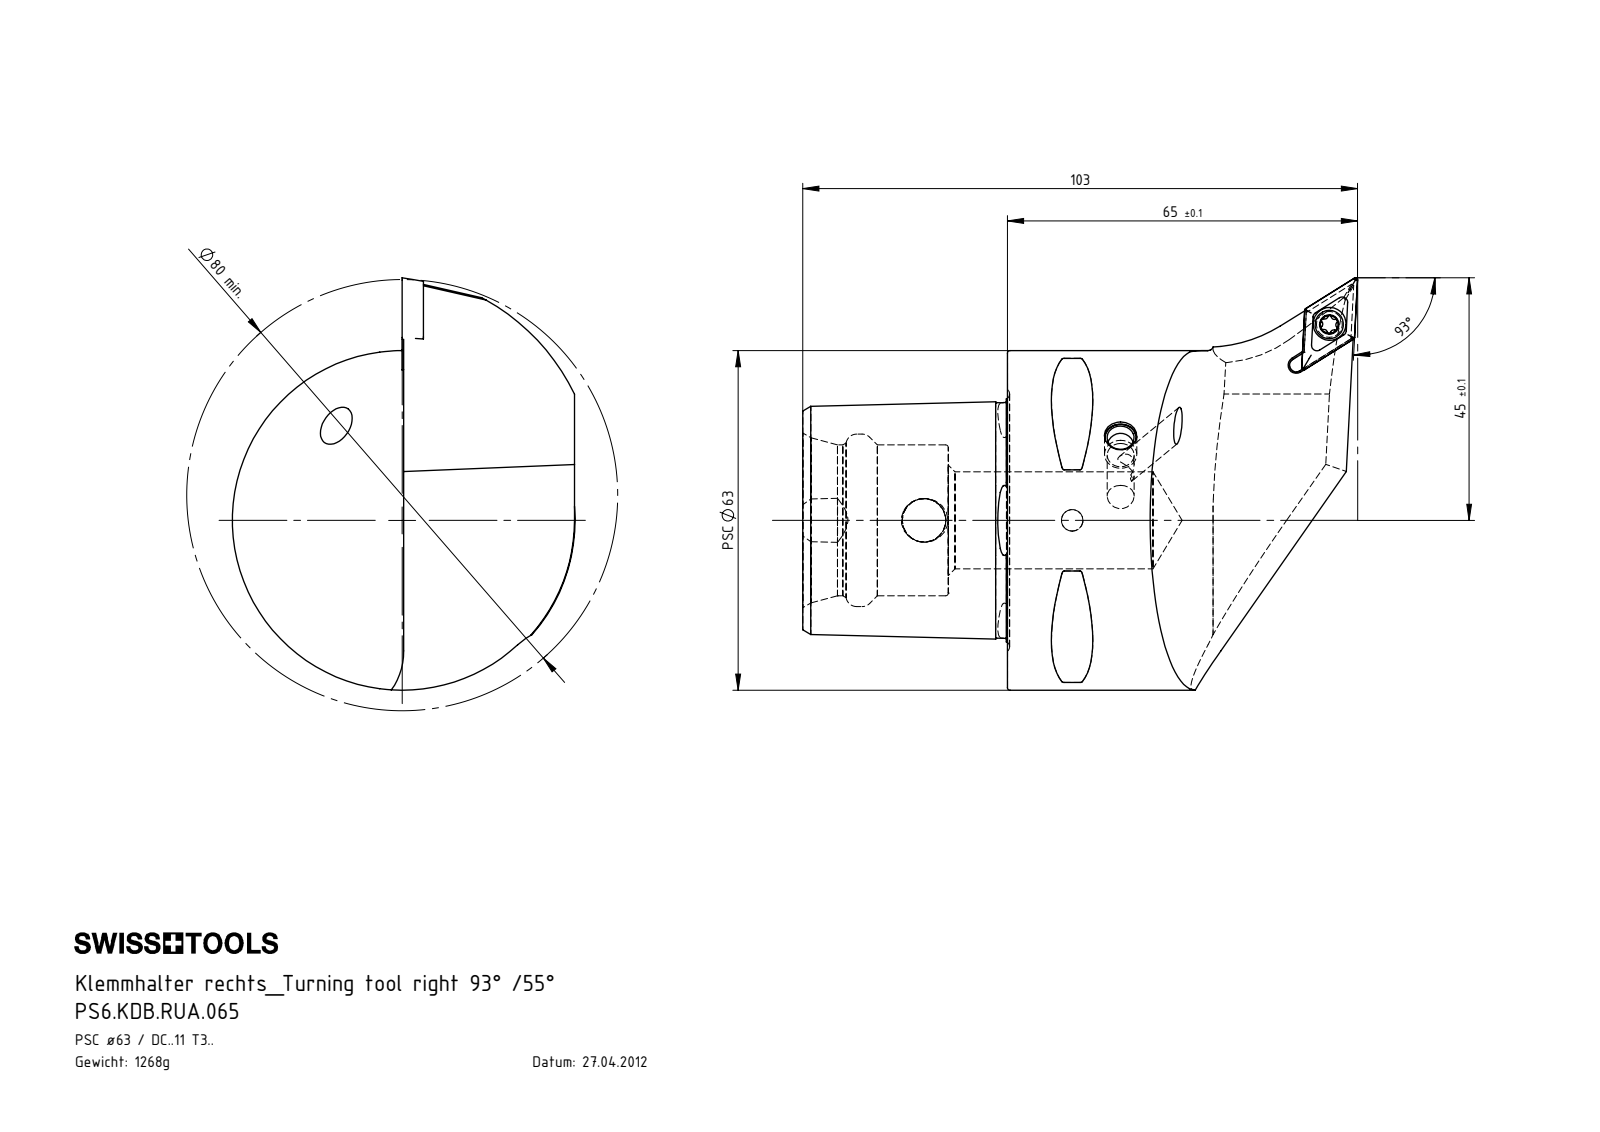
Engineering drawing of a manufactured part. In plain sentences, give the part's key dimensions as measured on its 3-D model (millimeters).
The part is named "PS6.KDB.RUA.065; KVT_MB_600_060; DCMT11T304; WCB-ER2.001.009_A (+1 more)". Its 3-D file was written by "SolidWorks 2017 (AUTOMOTIVE_DESIGN)". It is 5 solids with 199 faces: 53 planar, 45 cylindrical and 101 other. Overall it measures 103 by 76.51 by 63.61 millimeters. Its volume is 161 267 cubic millimeters and its surface area 28 091 square millimeters. Round holes: 2 of diameter 5, 1 of diameter 3.3, 1 of diameter 4, 1 of diameter 4.4, 1 of diameter 6.1, 1 of diameter 8.1, 1 of diameter 18, 1 of diameter 28, 1 of diameter 32. Round bosses or shafts: 1 of diameter 63, 1 of diameter 6, 1 of diameter 5.25, 1 of diameter 4. Partial cylindrical surfaces (rounded edges, fillets, slot ends): 8 of radius 0.5, 6 of radius 0.34, 6 of radius 0.59, 2 of radius 6, 1 of radius 1.25, 1 of radius 26, 1 of radius 32, 1 of radius 40. The main face-to-face distances are 31.7, 38, 24.88, 27, 11, 55.8, 28.03, 3.67, 37.8, 10.8. The hole center spacings are 27.5, 60, 60.12, 83.56, 83.66.
